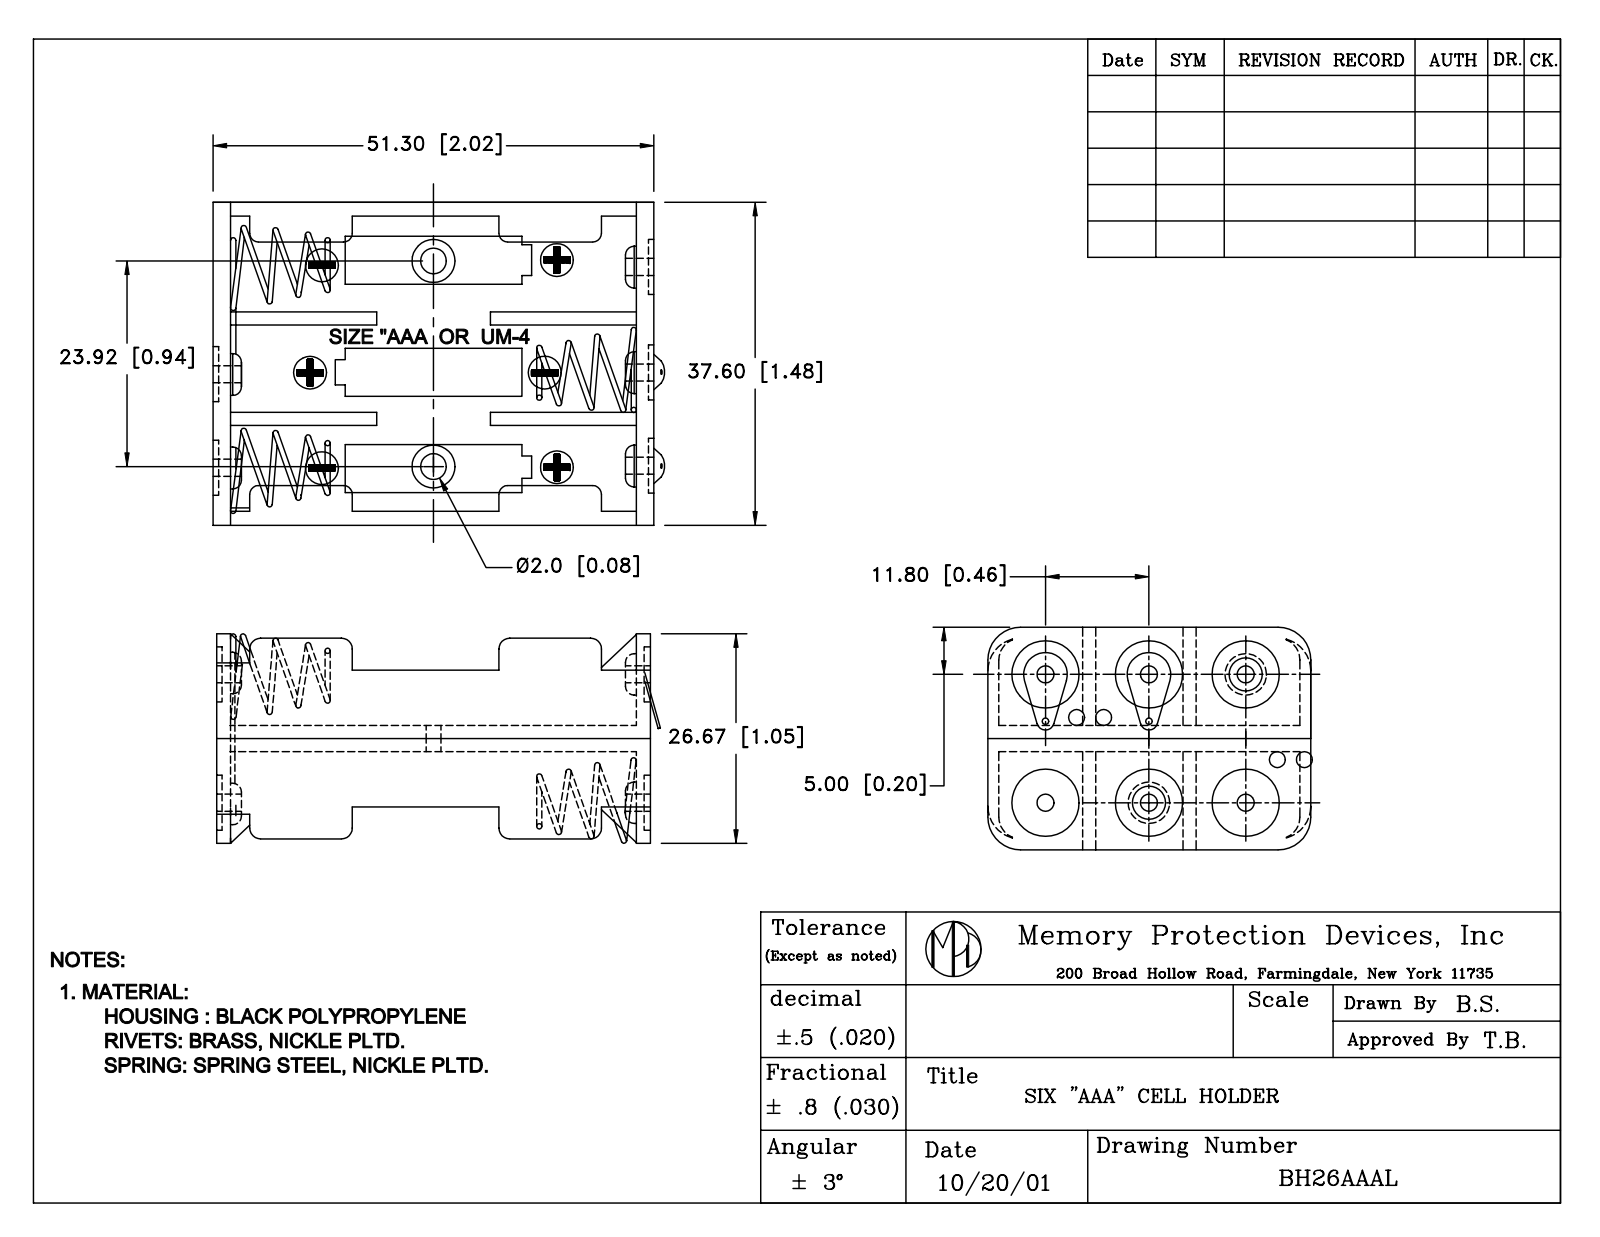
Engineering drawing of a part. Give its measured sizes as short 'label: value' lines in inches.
name: BH26AAAL
written by: SolidWorks 2017 (AUTOMOTIVE_DESIGN)
unit: in
bodies: 13 solids, 1007 faces (440 planar, 341 cylindrical, 226 other)
size: 2.127 × 1.48 × 1.05
volume: 0.652 in³; area: 23.83 in²
holes: 6× ⌀0.087, 6× ⌀0.091, 6× ⌀0.118, 6× ⌀0.146, 6× ⌀0.299, 4× ⌀0.079, 2× ⌀0.031
bosses: 6× ⌀0.244, 6× ⌀0.185, 6× ⌀0.138, 4× ⌀0.024
rounds: 24× R0.008, 16× R0.098, 4× R0.157, 4× R0.177, 4× R0.207, 2× R0.055, 2× R0.118, 1× R0.354
face distances: 0.043, 0.122, 1.976, 1.437, 1.933, 1.48, 2.02, 1.393, 0.485, 0.952
hole spacings: 0.512, 1.086, 0.465, 0.657, 1.024, 0.285, 0.372, 0.462
